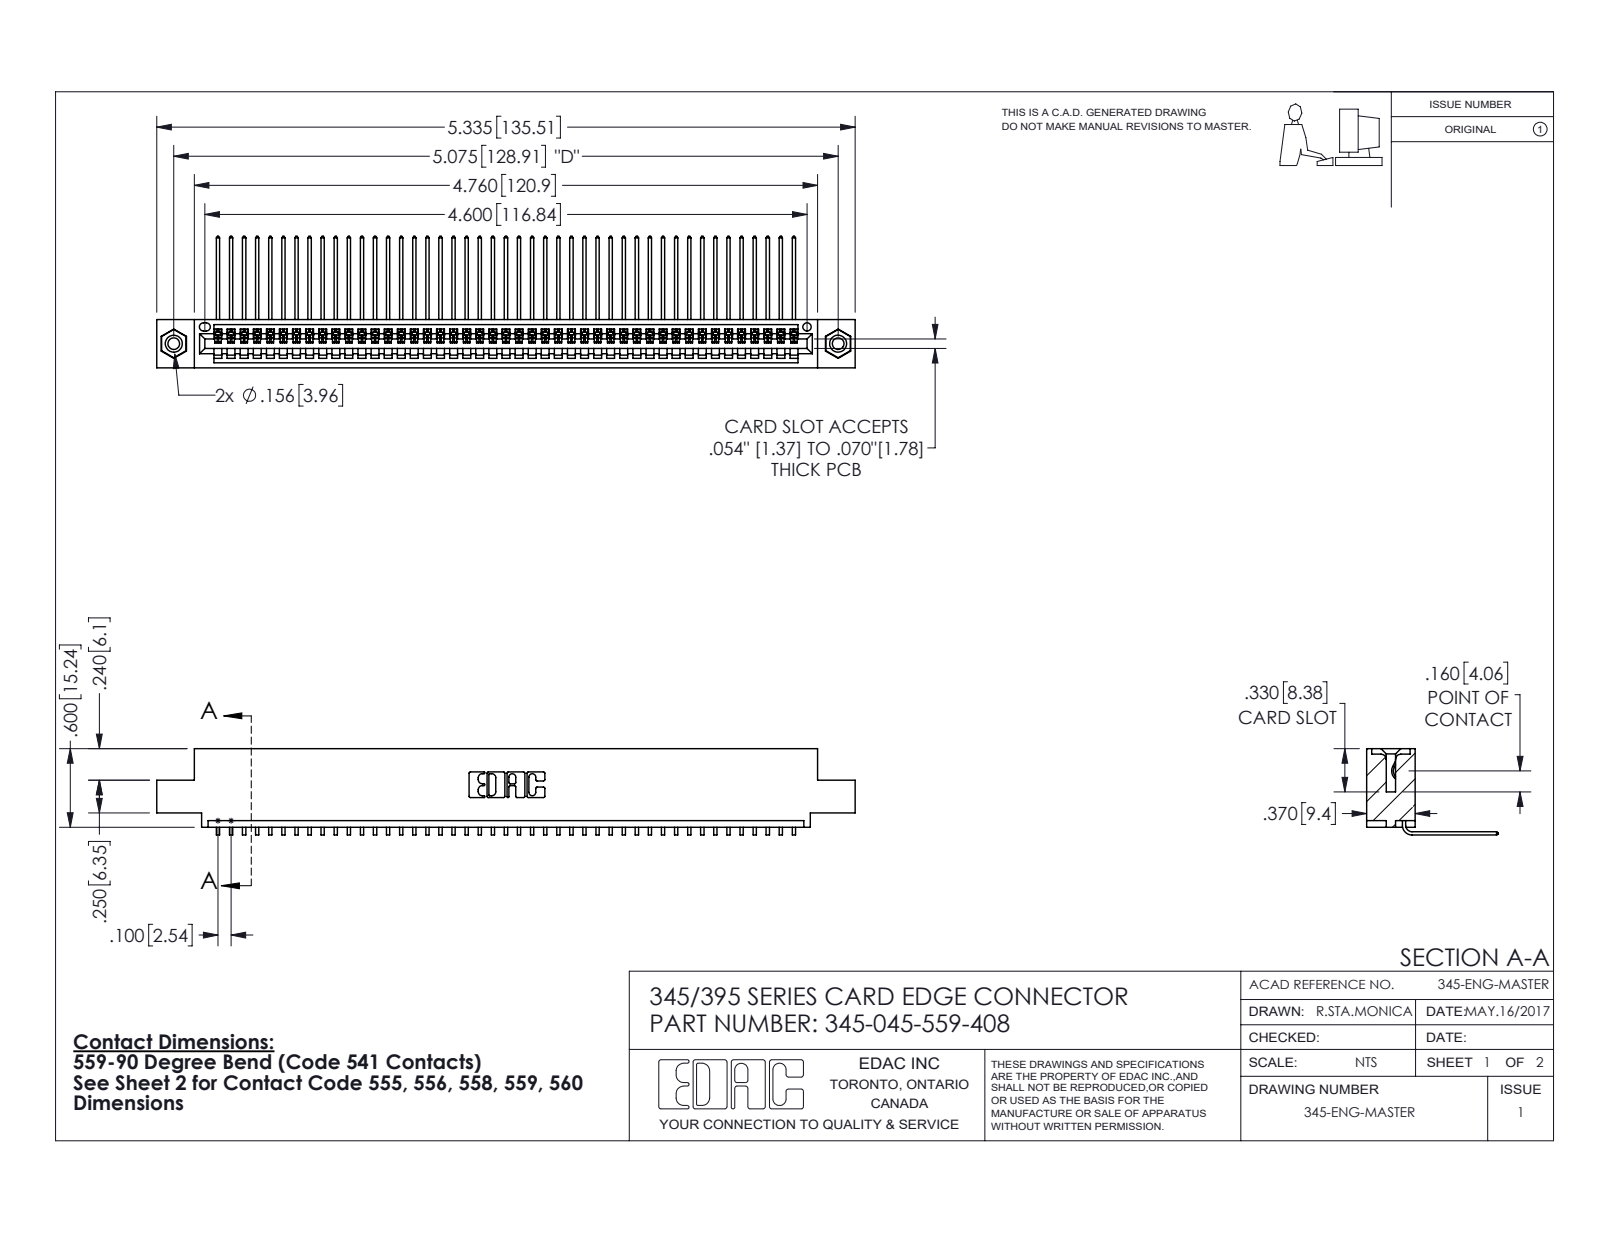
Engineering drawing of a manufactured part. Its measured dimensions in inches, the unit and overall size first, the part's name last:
Units: inches
Overall size (bounding box): 5.335 × 1.005 × 0.659
Round holes (diameter × count): ⌀0.089 ×2, ⌀0.125 ×2, ⌀0.156 ×2, ⌀0.064 ×1
Round bosses / shafts (diameter × count): ⌀0.155 ×2
Partial cylindrical surfaces — rounded edges, fillets, slot ends (radius × count): R0.006 ×90, R0.01 ×22, R0.007 ×6, R0.031 ×6, R0.026 ×3, R0.031 ×2, R0.04 ×2, R0.014 ×1
Main face-to-face distances: 0.072, 0.298, 0.37, 0.2, 0.098, 0.272, 0.025, 0.225, 0.149, 0.072
Hole centre spacings: 0.27, 4.839, 5.075
Volume: 0.791 in³ · Surface area: 28.29 in²
Bodies: 48 solids, 2890 faces (2006 planar, 868 cylindrical, 16 other)
Part name (STEP PRODUCT): 345 Part_0.110 Offset - 0.156 Dia-TI; 345-045-559-408; 345-292-001_558 559 Tail - 1; 345-250-001_345-250-003-102
STEP written by: SolidWorks 2016 (CONFIG_CONTROL_DESIGN)
